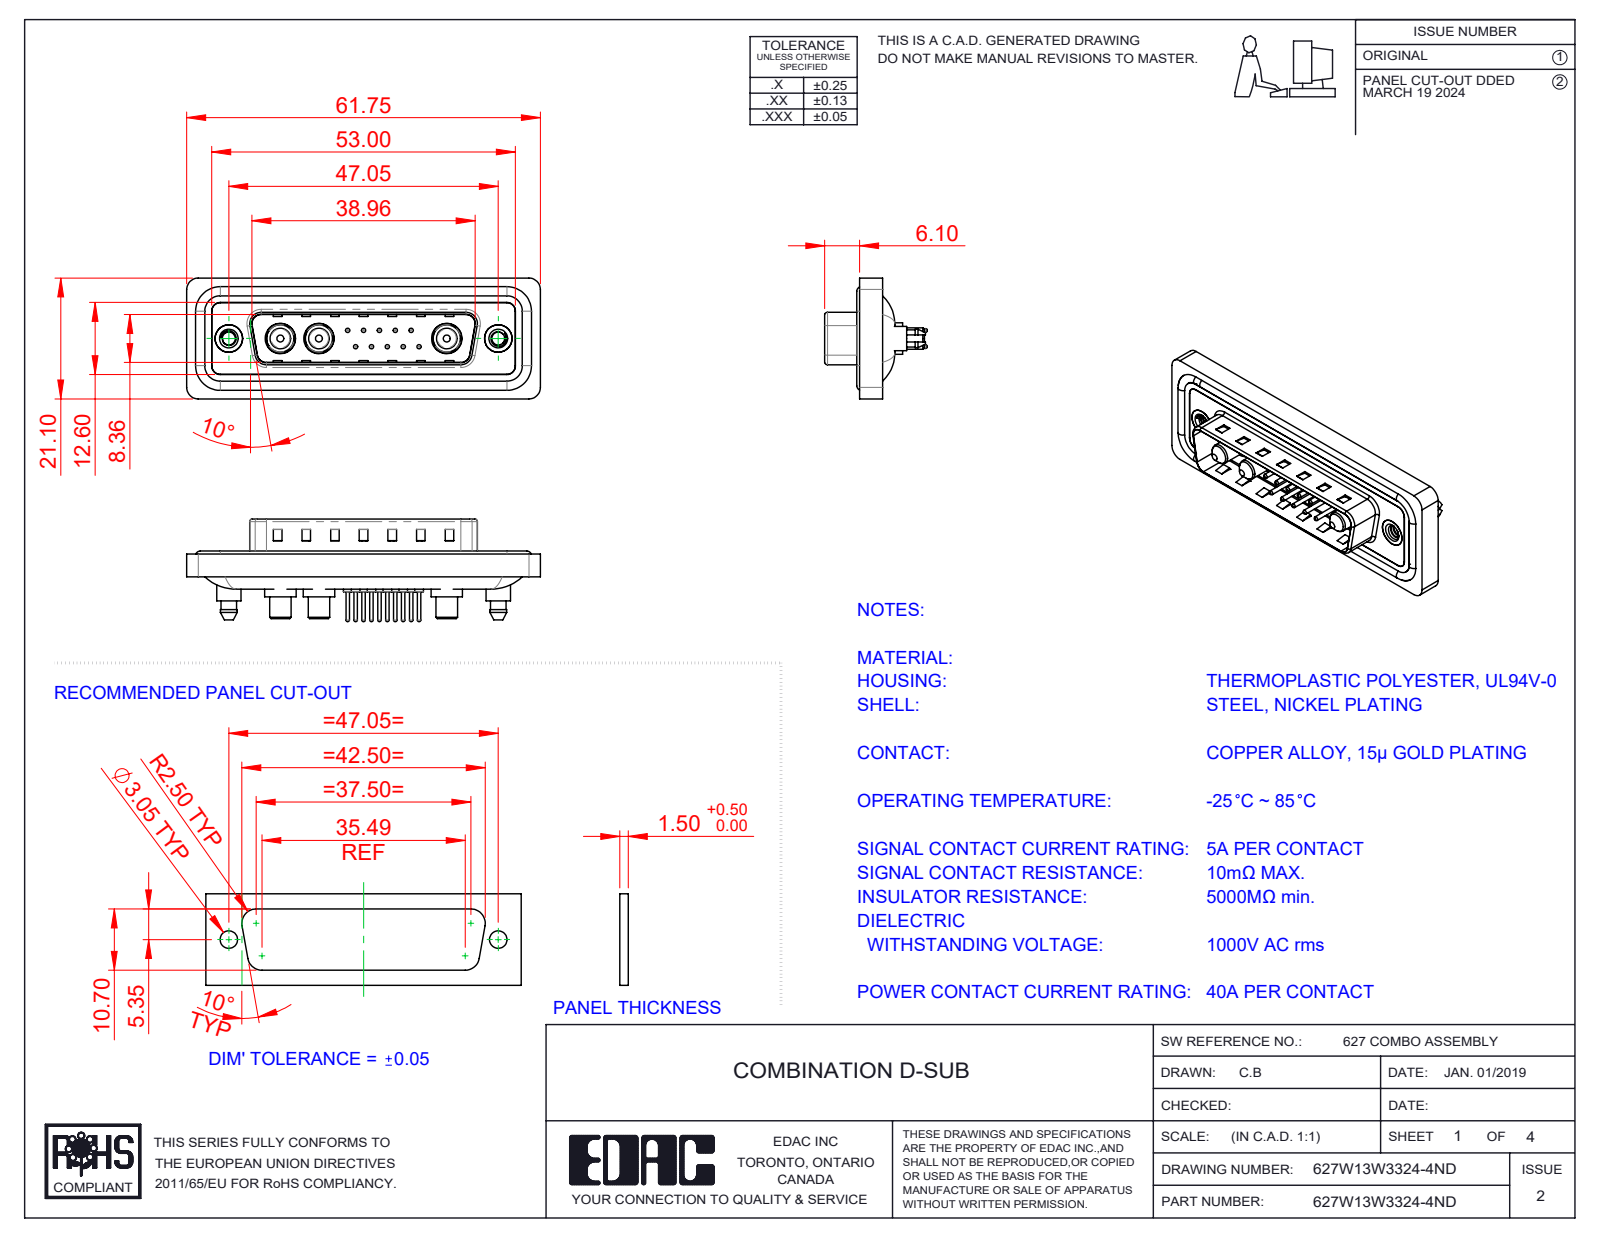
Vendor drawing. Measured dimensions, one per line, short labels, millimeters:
name: 627Combo Shell Front_25 Contacts; Power Pin_40A S; 627Combo Housing_13W3; 627Combo Waterproof Housing_25 Contacts (+6 more)
written by: SolidWorks 2023 (CONFIG_CONTROL_DESIGN)
unit: mm
bodies: 23 solids, 1028 faces (325 planar, 425 cylindrical, 278 other)
size: 61.75 × 21.1 × 17.9
volume: 7 525 mm³; area: 12 244 mm²
holes: 10× ⌀0.75, 10× ⌀1.6, 10× ⌀2, 3× ⌀4.85, 3× ⌀5.3, 2× ⌀2.26, 2× ⌀4, 2× ⌀4.8, 2× ⌀5
bosses: 10× ⌀1.5, 10× ⌀0.6, 4× ⌀1.6, 3× ⌀5.5, 3× ⌀5.2, 3× ⌀4.75, 3× ⌀3.75, 3× ⌀3.6
rounds: 24× R1.5, 18× R2, 10× R1.6, 8× R0.5, 4× R0.25, 4× R0.6, 4× R0.65, 4× R0.9
face distances: 0.4, 1.5, 1.1, 1.6, 0.5, 3.1, 2.9, 0.82, 9.58, 4.1
hole spacings: 3.16, 2.77, 5.04, 5.54, 7.49, 5.03, 8.31, 10.11
